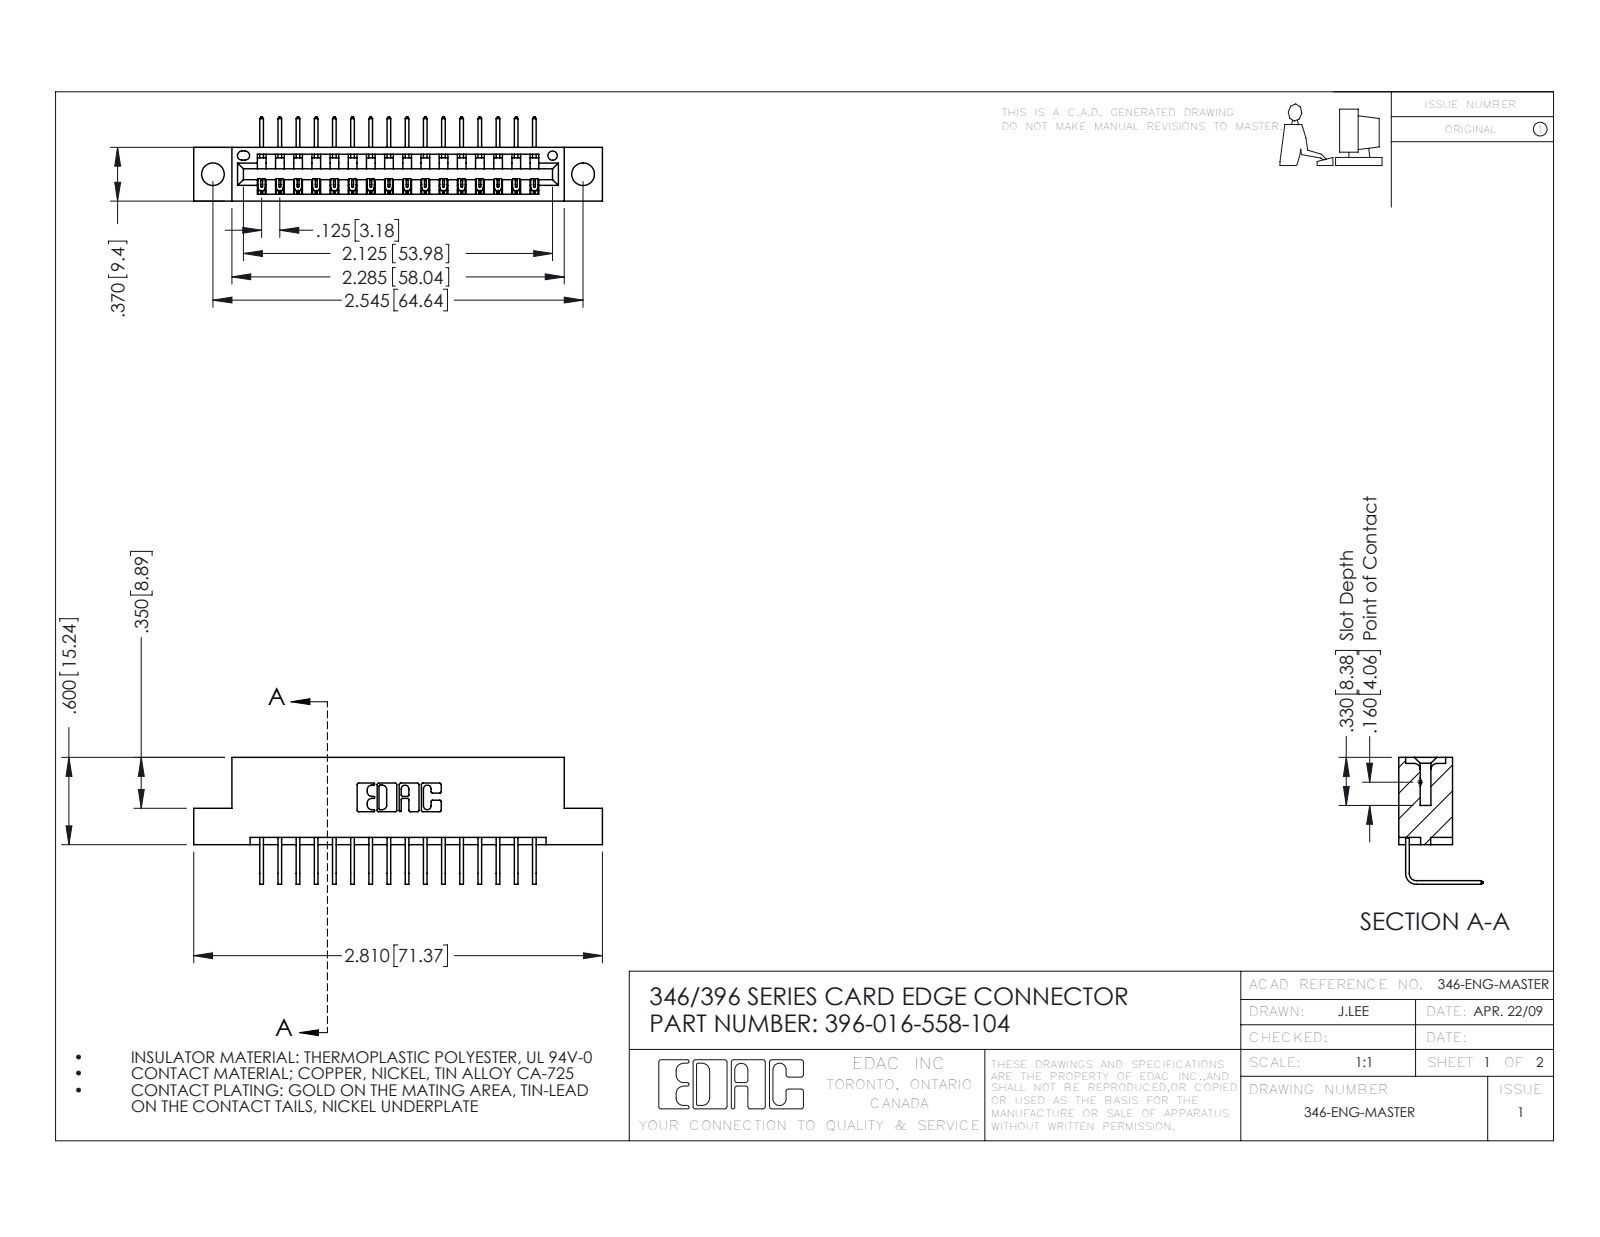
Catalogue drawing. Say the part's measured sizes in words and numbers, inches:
The part is named "346 Part_Flush Mounting Lugs - 0.156 Dia-TH; 396-016-558-104; 345-292-001_558 Tail - 2". Its 3-D file was written by "SolidWorks 2016 (CONFIG_CONTROL_DESIGN)". It is 17 solids with 1082 faces: 748 planar, 334 cylindrical and 0 other. Overall it measures 2.81 by 0.873 by 0.58 inches. Its volume is 0.404 cubic inches and its surface area 12.58 square inches. Round holes: 2 of diameter 0.156, 1 of diameter 0.064. Partial cylindrical surfaces (rounded edges, fillets, slot ends): 32 of radius 0.006, 22 of radius 0.01, 6 of radius 0.007, 6 of radius 0.031, 3 of radius 0.026, 2 of radius 0.031, 2 of radius 0.04, 1 of radius 0.014. The main face-to-face distances are 0.322, 0.048, 0.25, 0.37, 0.298, 0.025, 0.072, 0.148, 0.222, 0.1. The hole center spacings are 0.246, 2.338, 2.545.
